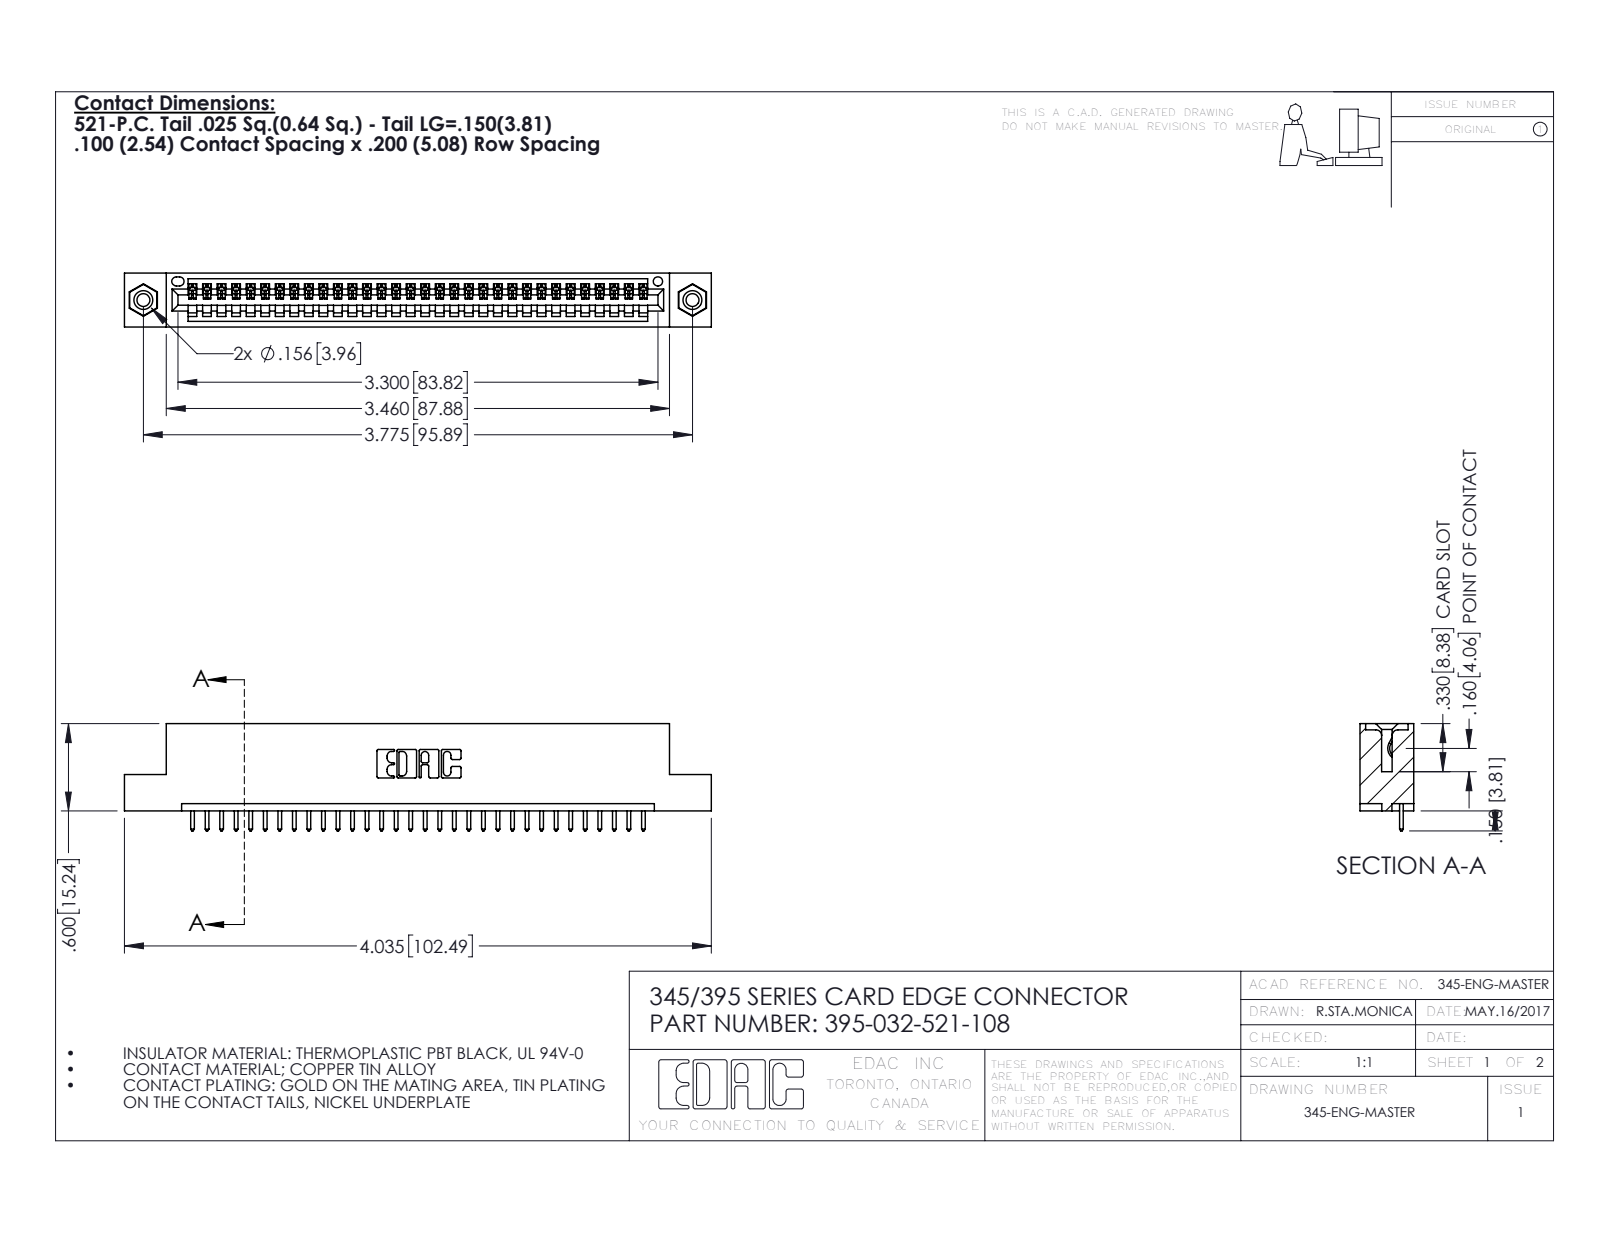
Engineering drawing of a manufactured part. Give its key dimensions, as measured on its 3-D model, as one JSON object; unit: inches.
{"part_name": "345 Part_Flush Mounting Lugs - 0.156 Dia-TI; 345-292-001_345-293-121; 395-032-521-108; 345-250-001_345-250-003-102", "step_written_by": "SolidWorks 2016 (CONFIG_CONTROL_DESIGN)", "units": "inches", "bodies": {"solids": 35, "faces": 2042, "planar": 1392, "cylindrical": 634, "other": 16}, "overall_size": [4.035, 0.737, 0.37], "volume_in3": 0.583, "surface_area_in2": 18.95, "round_holes": [[0.089, 2], [0.125, 2], [0.156, 2], [0.064, 1]], "round_bosses_or_shafts": [[0.155, 2]], "partial_cylinders_radius": [[0.006, 64], [0.01, 64], [0.01, 22], [0.007, 6], [0.031, 6], [0.026, 3], [0.031, 2], [0.04, 2]], "face_to_face_distances": [0.072, 0.298, 0.2, 0.37, 0.098, 0.272, 0.025, 0.225, 0.149, 0.072], "hole_center_spacings": [0.27, 3.54, 3.775]}
